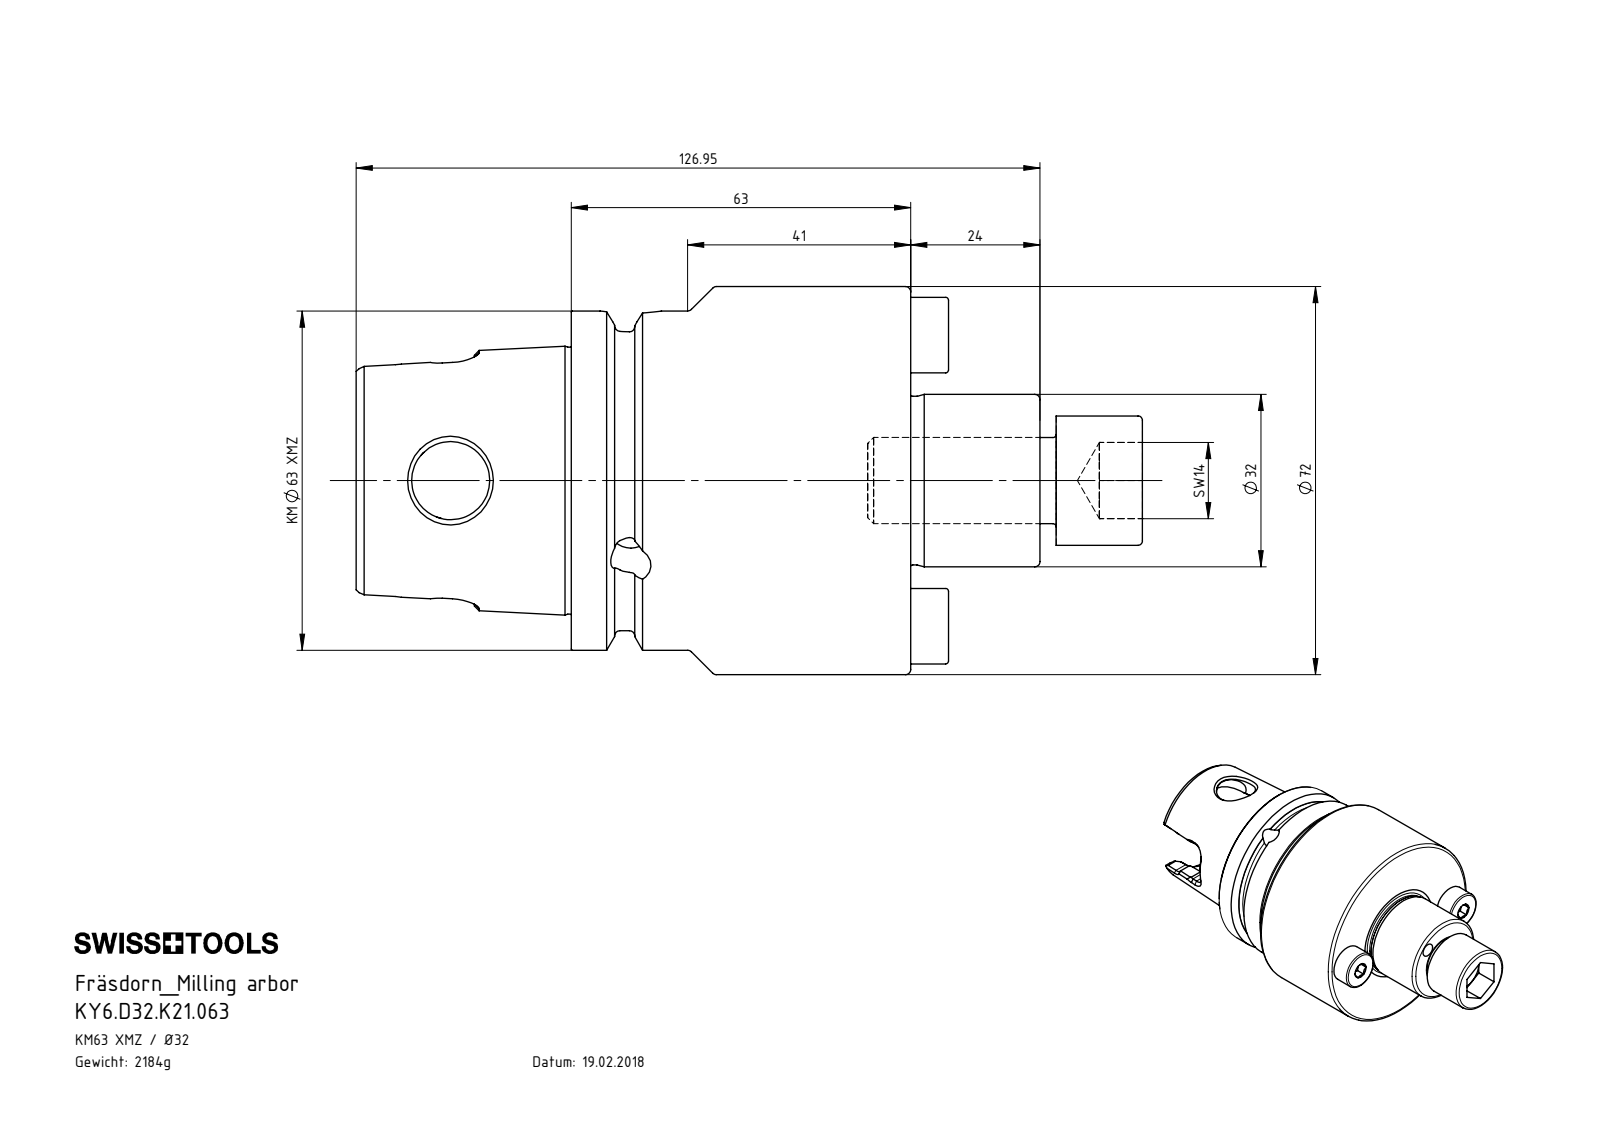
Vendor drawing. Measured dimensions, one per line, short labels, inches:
name: KY6.D32.K21.063; D32-ER1.002.035_A; KY6-D32.K21.063_B; D32-ER2.001.022_B
written by: SolidWorks 2017 (CONFIG_CONTROL_DESIGN)
unit: in
bodies: 4 solids, 387 faces (86 planar, 102 cylindrical, 199 other)
size: 5.746 × 2.835 × 2.835
volume: 16.98 in³; area: 69.67 in²
holes: 5× ⌀0.197, 2× ⌀0.294, 2× ⌀0.472, 1× ⌀0.268, 1× ⌀0.334, 1× ⌀0.394, 1× ⌀0.453, 1× ⌀0.551, 1× ⌀0.571, 1× ⌀0.669, 1× ⌀1.224, 1× ⌀1.389
bosses: 2× ⌀0.551, 2× ⌀0.236, 2× ⌀0.181, 1× ⌀2.835, 1× ⌀2.478, 1× ⌀2.193, 1× ⌀1.26, 1× ⌀1.232
rounds: 8× R0.157, 2× R0.277
face distances: 2.48, 0.043, 2.524, 0.236, 0.118, 3.469, 3.425, 0.945, 1.26, 2.992
hole spacings: 0.482, 0.798, 1.063, 1.445, 0.964, 2.126
